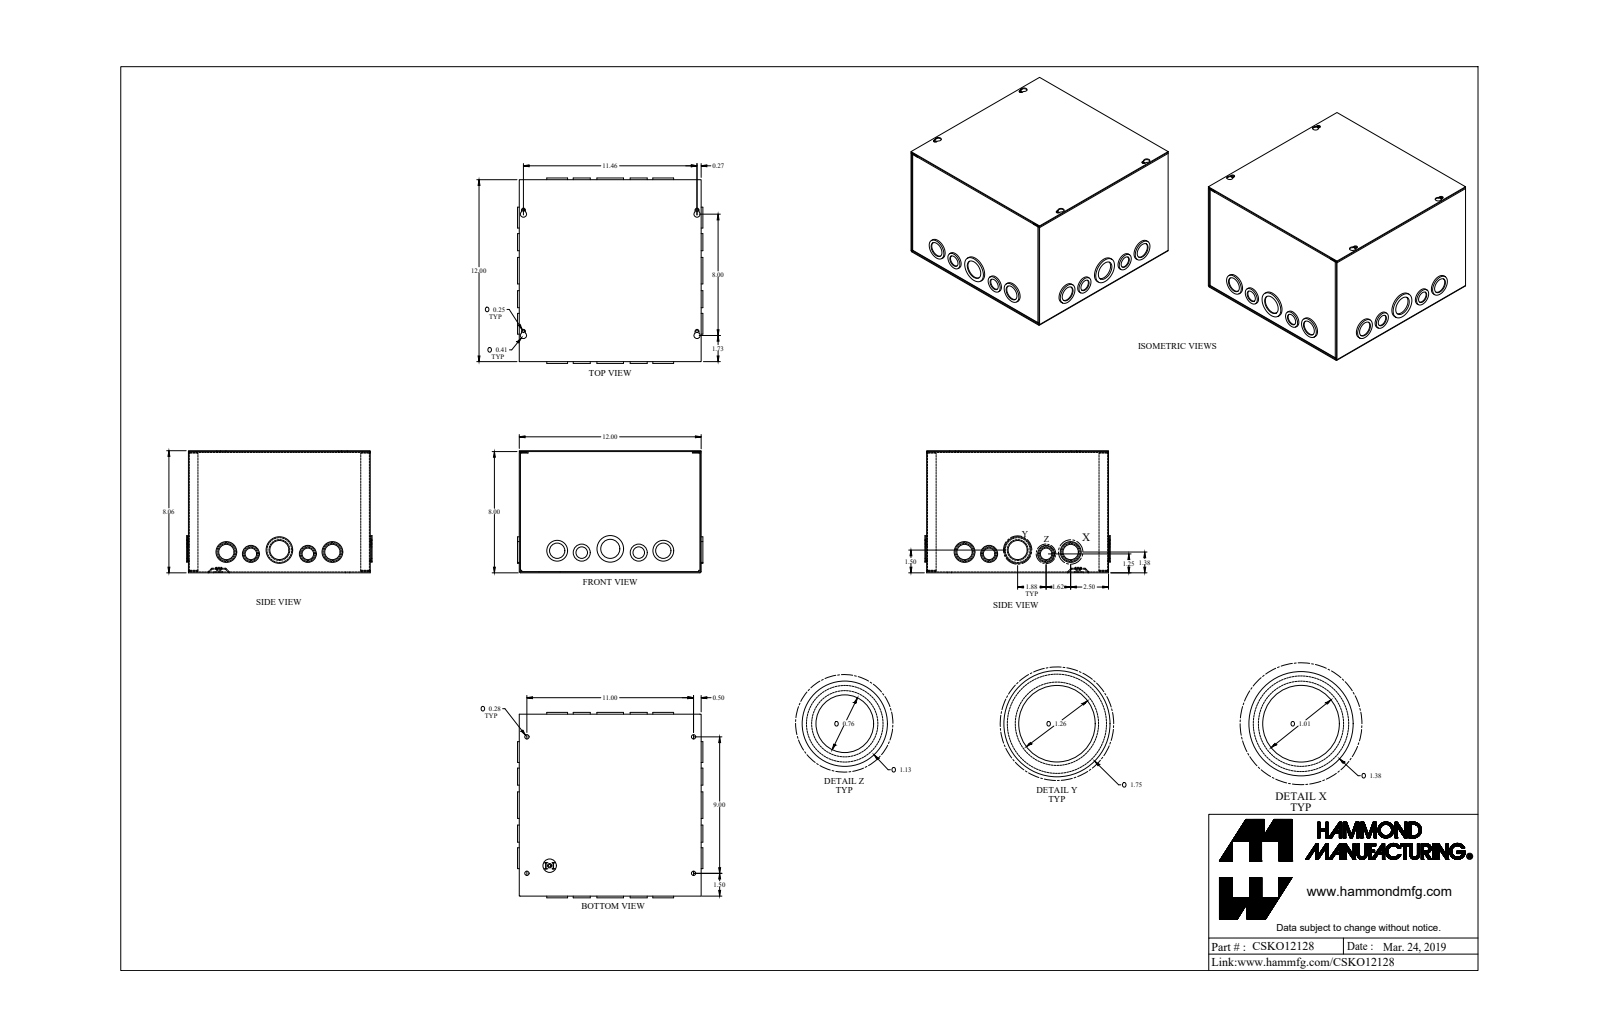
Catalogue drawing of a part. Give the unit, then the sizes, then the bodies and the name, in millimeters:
Units: millimetres
Overall size (bounding box): 310.7 × 310.7 × 204.6
Round holes (diameter × count): ⌀25.7 ×8, ⌀32 ×6, ⌀4.3 ×5, ⌀7.1 ×4, ⌀19.3 ×4, ⌀41.6 ×2, ⌀12.7 ×1
Round bosses / shafts (diameter × count): ⌀28.6 ×6, ⌀34.9 ×5, ⌀22.2 ×4, ⌀22.2 ×4, ⌀44.5 ×2, ⌀28.6 ×2, ⌀34.9 ×1, ⌀12.5 ×1
Partial cylindrical surfaces — rounded edges, fillets, slot ends (radius × count): R0.7 ×12, R2.2 ×12, R1.4 ×8, R3.2 ×4, R5.2 ×4
Main face-to-face distances: 1.4, 303.4, 203.2, 304.8, 301.9, 201.8, 204.6, 1.8, 301.6, 2.9
Hole centre spacings: 14, 41.3, 48.2, 89, 136.7, 216, 285.5, 357.7
Volume: 679 600 mm³ · Surface area: 947 100 mm²
Bodies: 4 solids, 445 faces (205 planar, 232 cylindrical, 8 other)
Part name (STEP PRODUCT): CSKO12128_Default
STEP written by: SolidWorks 2019 (CONFIG_CONTROL_DESIGN)
